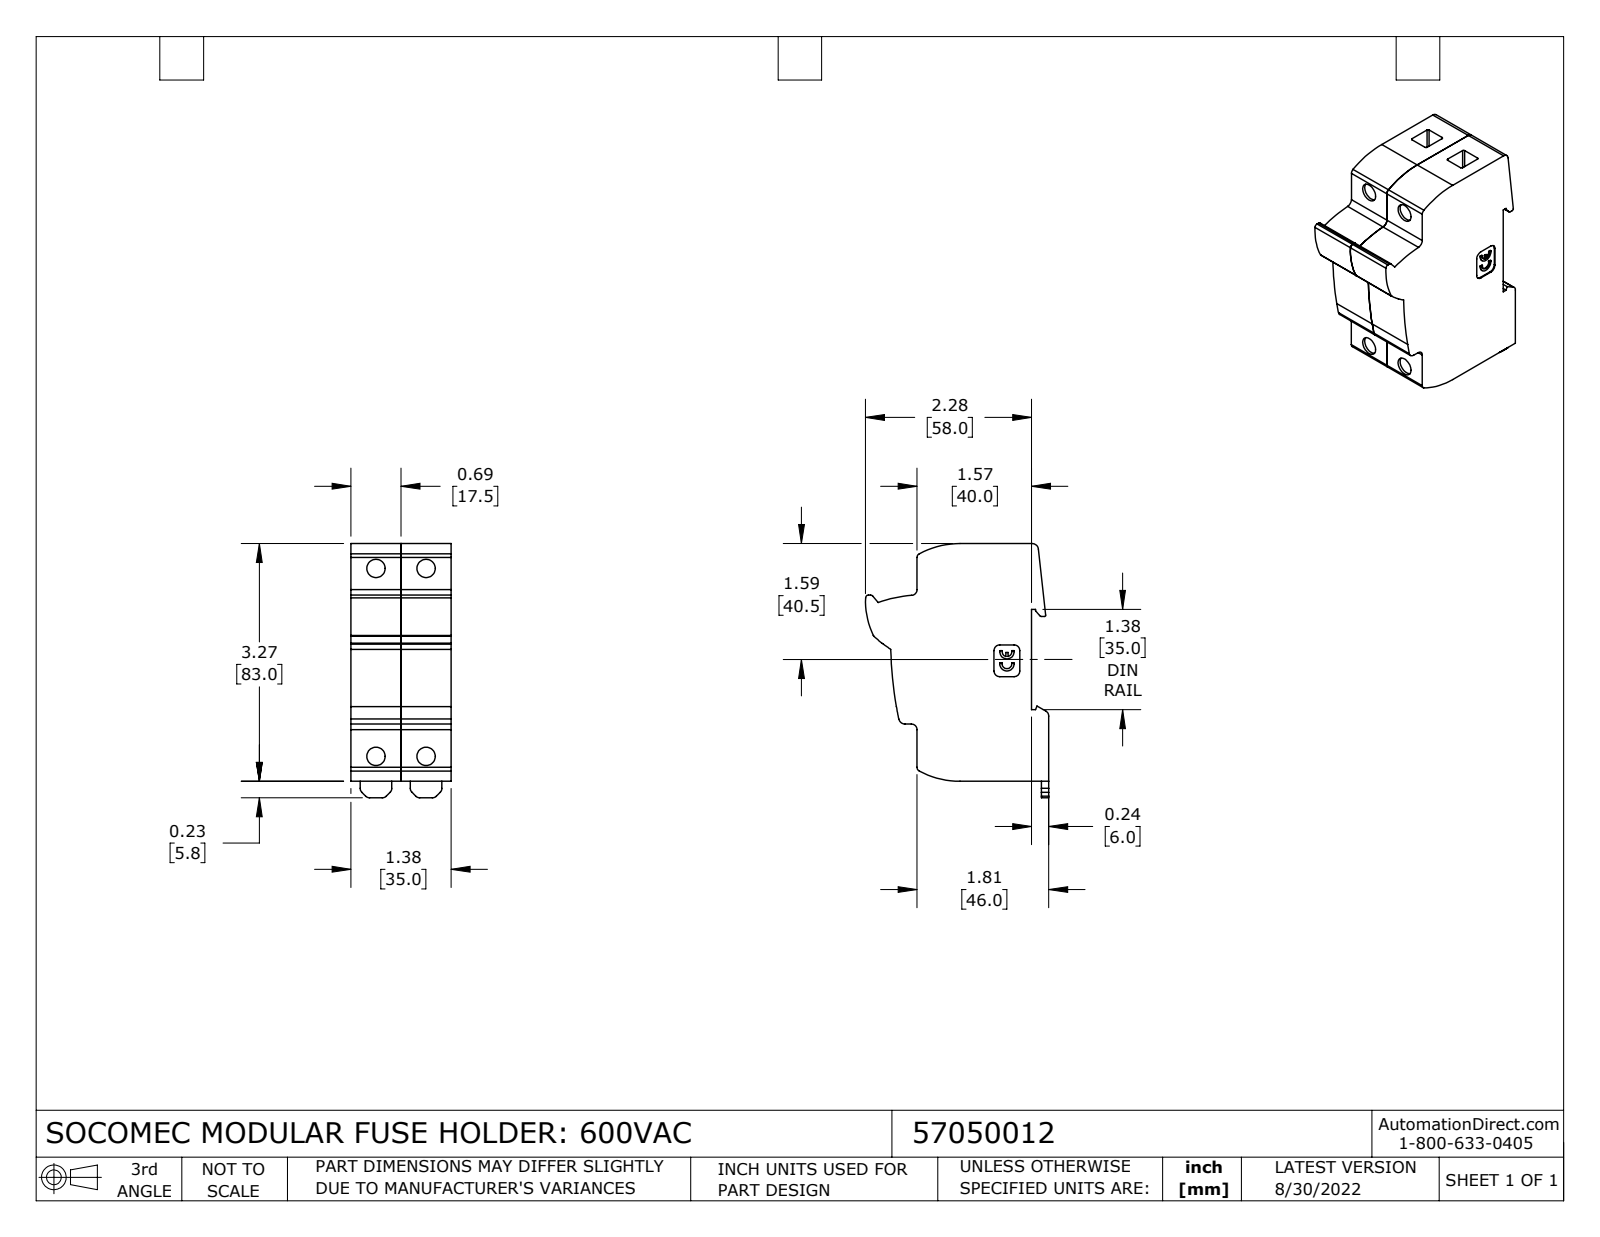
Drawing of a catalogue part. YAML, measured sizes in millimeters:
part_name: "57050012"
step_written_by: "SolidWorks 2021 (CONFIG_CONTROL_DESIGN)"
units: millimeters
bodies: {solids: 2, faces: 210, planar: 104, cylindrical: 106, other: 0}
overall_size: [88.8, 64, 35]
volume: 138600
surface_area: 27520
round_holes:
  - {diameter: 6.4, count: 4}
partial_cylinders:
  - {radius: 2, count: 15}
  - {radius: 0.5, count: 9}
  - {radius: 1, count: 4}
  - {radius: 1.5, count: 2}
  - {radius: 1.7, count: 2}
  - {radius: 2.2, count: 2}
  - {radius: 2.5, count: 2}
  - {radius: 30.1, count: 2}
face_to_face_distances: [17.5, 35, 6, 40, 83, 46, 5.1, 12.4, 22.6, 29.9]
hole_center_spacings: [17.5, 65.6, 67.9]
